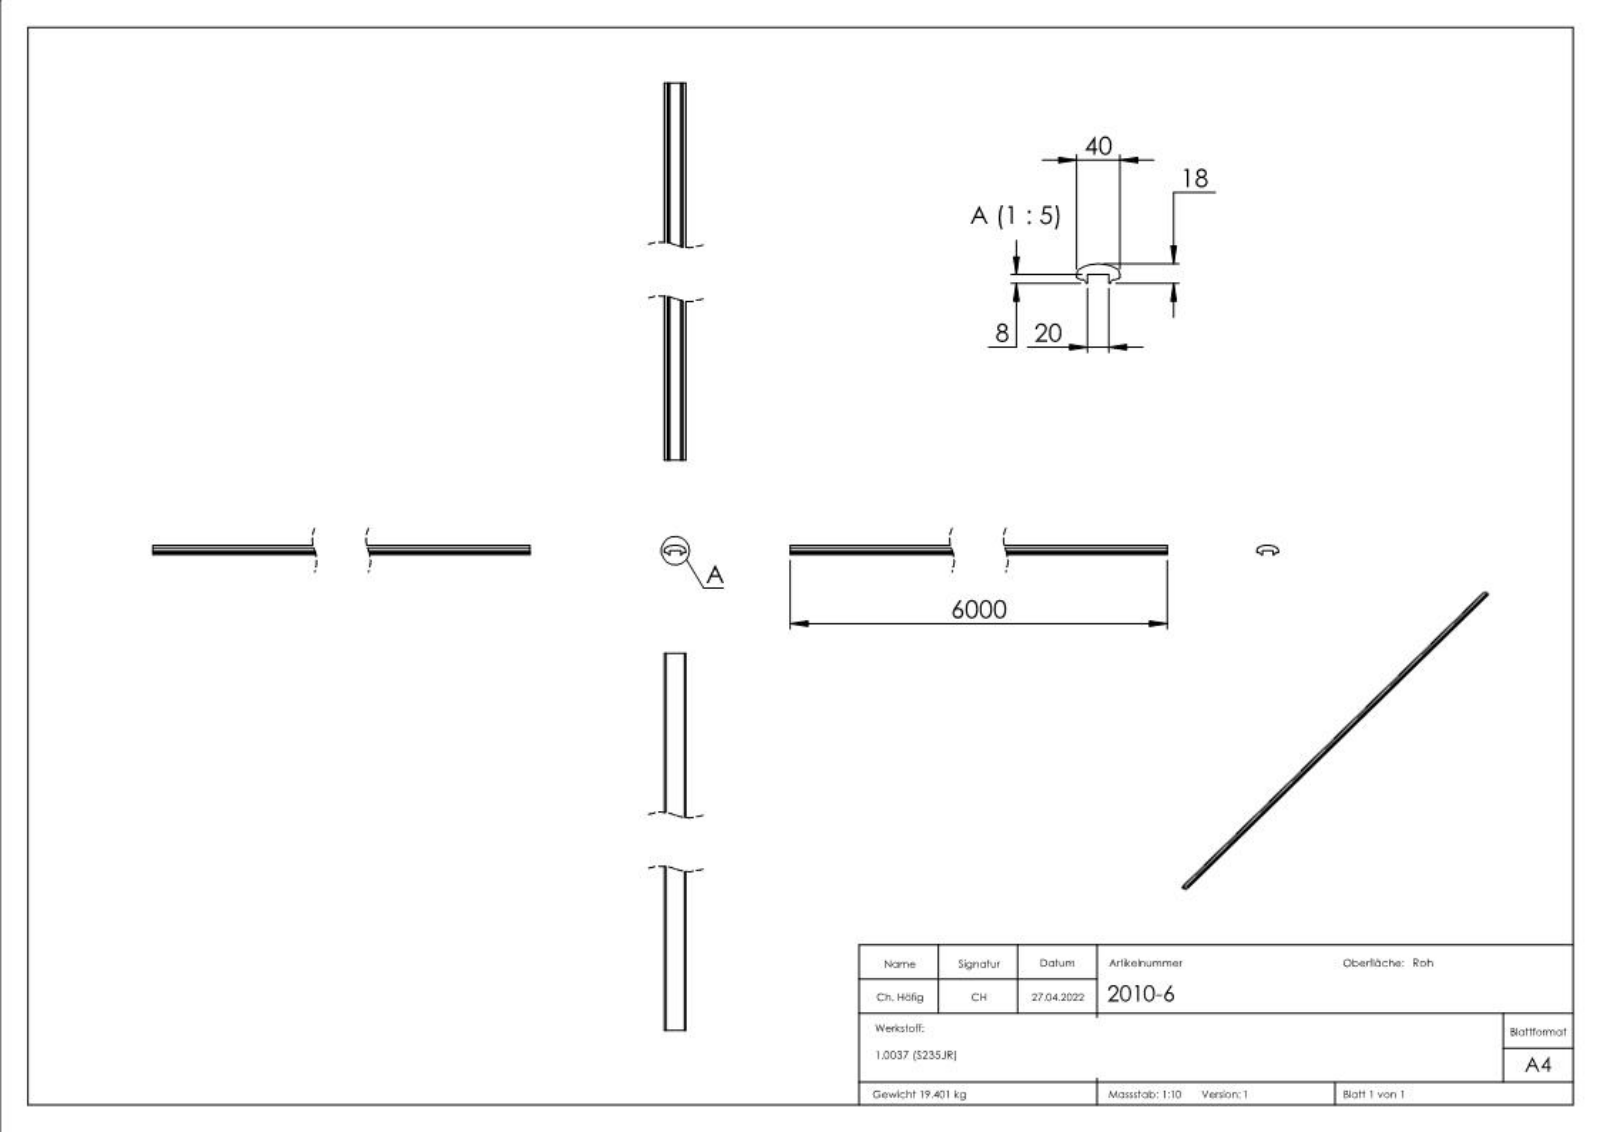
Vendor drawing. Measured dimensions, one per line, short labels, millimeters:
name: 2010-6
written by: SolidWorks 2018 (CONFIG_CONTROL_DESIGN)
unit: mm
bodies: 1 solid, 237 faces (125 planar, 11 cylindrical, 101 other)
size: 6000 × 40 × 18
volume: 2 536 000 mm³; area: 695 559 mm²
rounds: 4× R1, 2× R3.1, 2× R6, 2× R10, 1× R33
face distances: 18.5, 10.75, 29.25, 8.5, 40, 6000, 8.6, 1.14, 3.92, 0.58
